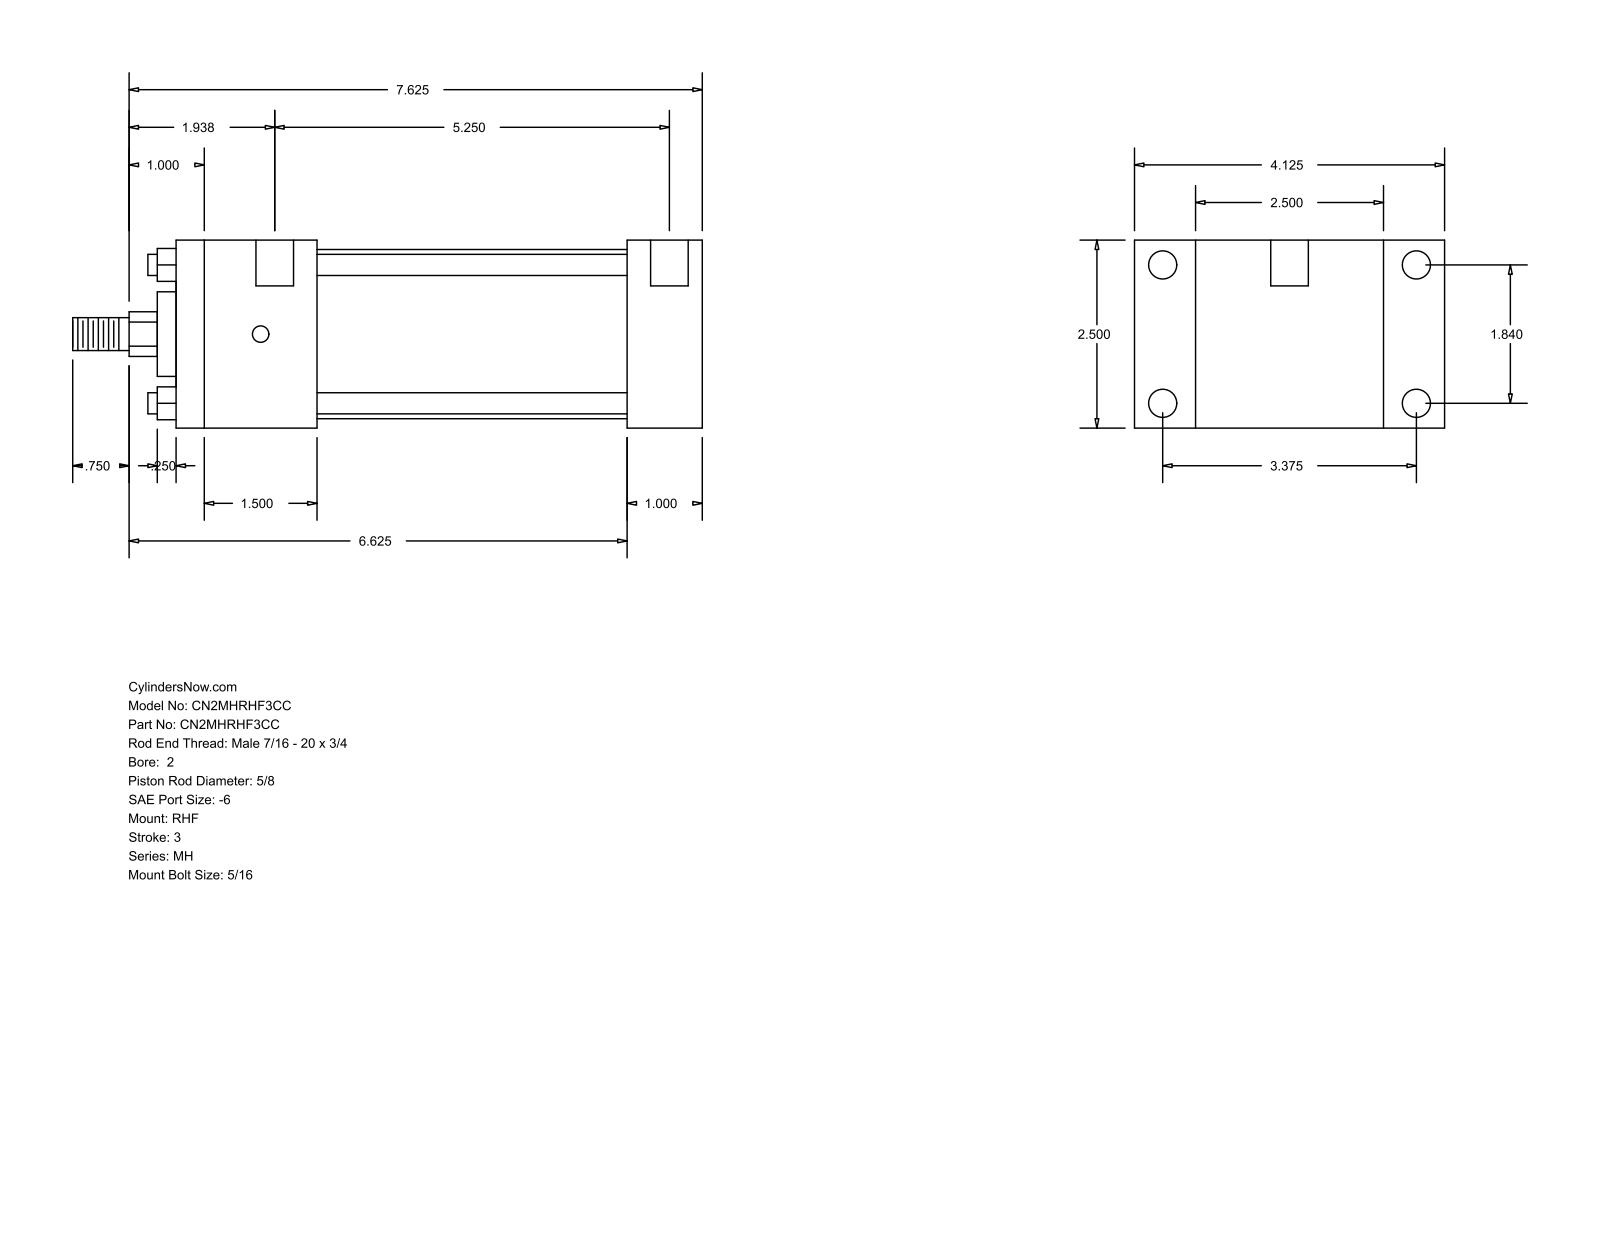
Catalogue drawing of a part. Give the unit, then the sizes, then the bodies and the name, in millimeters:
Units: millimetres
Overall size (bounding box): 212.72 × 104.78 × 63.5
Round holes (diameter × count): ⌀5.56 ×4, ⌀9.53 ×4, ⌀12.7 ×2
Round bosses / shafts (diameter × count): ⌀7.14 ×4, ⌀57.15 ×1, ⌀28.57 ×1, ⌀15.88 ×1, ⌀11.11 ×1
Partial cylindrical surfaces — rounded edges, fillets, slot ends (radius × count): R7.54 ×1
Main face-to-face distances: 63.5, 25.4, 20.64, 84.14, 152.4, 177.8, 104.78, 47.62, 130.18, 6.35
Hole centre spacings: 46.74, 85.72, 97.63, 141.29, 3.18, 4.76, 133.35, 136.53
Bodies: 0 solids, 88 faces (60 planar, 28 cylindrical, 0 other)
Part name (STEP PRODUCT): MH_RHF__0200_0.625
STEP written by: GSSL Pune (CONFIG_CONTROL_DESIGN)
